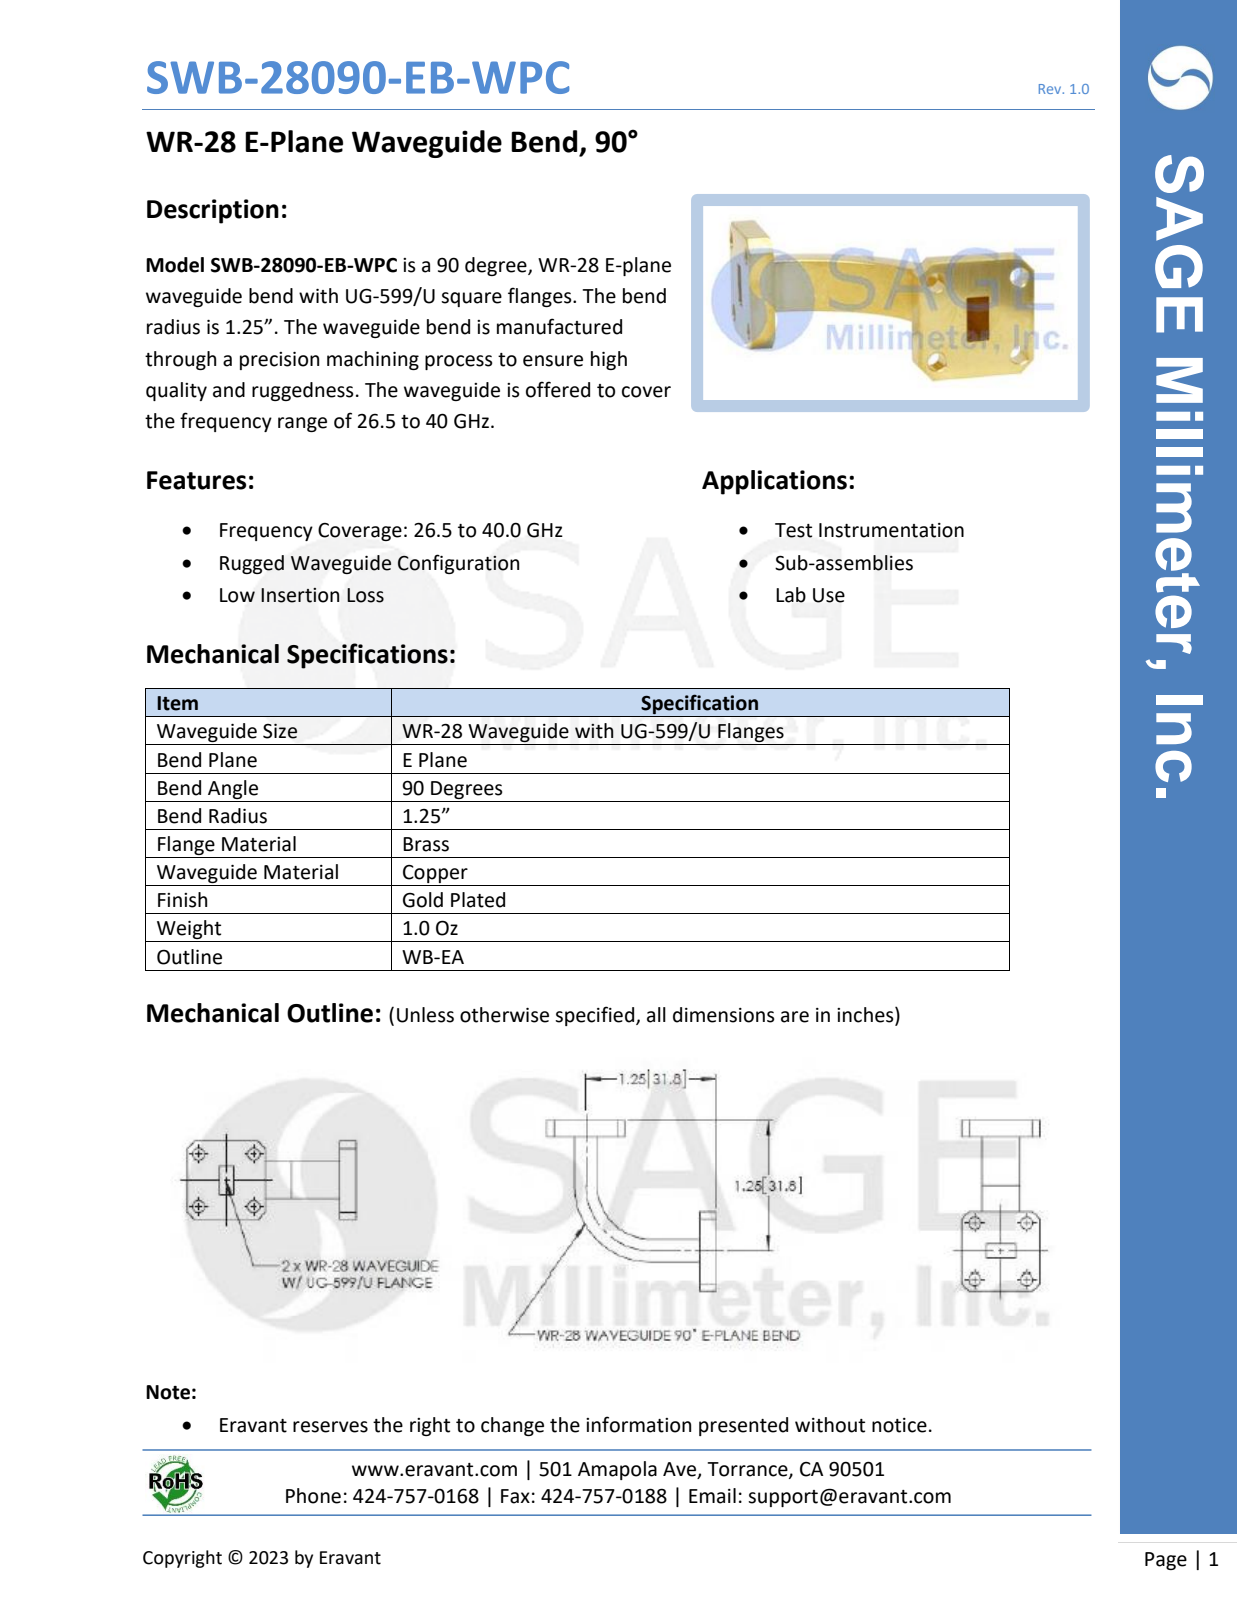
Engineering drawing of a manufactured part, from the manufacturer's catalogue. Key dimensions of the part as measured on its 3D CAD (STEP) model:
Part name (STEP PRODUCT): SWB-28090-EB-P
STEP written by: SolidWorks 2016 (AUTOMOTIVE_DESIGN)
Units: inches
Bodies: 1 solid, 52 faces (32 planar, 20 cylindrical, 0 other)
Overall size (bounding box): 1.69 × 1.625 × 0.88
Volume: 0.294 in³ · Surface area: 7.995 in²
Round holes (diameter × count): ⌀0.116 ×8
Partial cylindrical surfaces — rounded edges, fillets, slot ends (radius × count): R0.5 ×1, R0.54 ×1, R0.68 ×1, R0.72 ×1
Main face-to-face distances: 0.19, 0.04, 0.18, 0.32, 0.62, 0.36, 1.13, 1.32, 0.95, 1.14
Hole centre spacings: 0.5, 0.53, 0.64, 0.67, 0.729, 0.927
